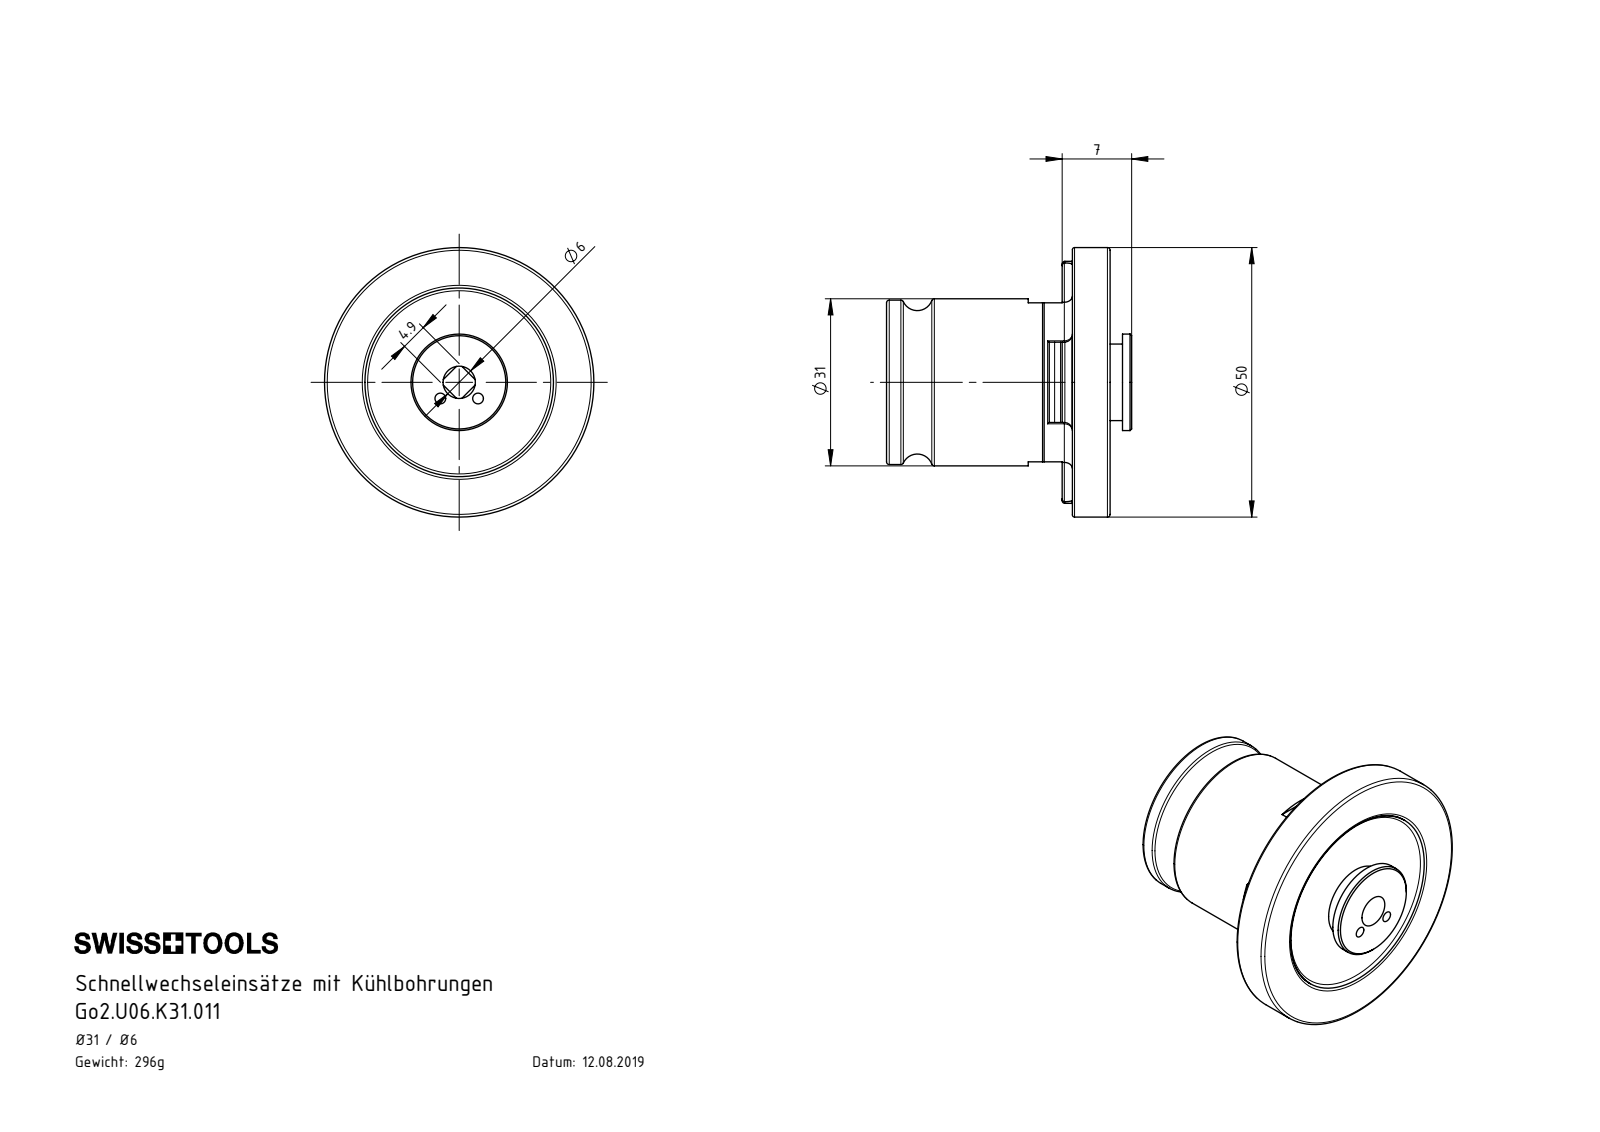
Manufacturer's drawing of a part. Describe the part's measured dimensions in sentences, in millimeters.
The part is named "Go2.U06.K31.011". Its 3-D file was written by "SolidWorks 2017 (AUTOMOTIVE_DESIGN)". It is 1 solid with 106 faces: 37 planar, 30 cylindrical and 39 other. Overall it measures 50 by 50 by 45.5 millimeters. Its volume is 37 719 cubic millimeters and its surface area 10 143 square millimeters. Round holes: 2 of diameter 2, 1 of diameter 6, 1 of diameter 20.1. Round bosses or shafts: 1 of diameter 50, 1 of diameter 35, 1 of diameter 31, 1 of diameter 30.6, 1 of diameter 30.5, 1 of diameter 17.9, 1 of diameter 14.2. Partial cylindrical surfaces (rounded edges, fillets, slot ends): 5 of radius 1.5, 4 of radius 0.5, 1 of radius 20, 1 of radius 22.45. The main face-to-face distances are 0.65, 6.35, 7, 34.5, 40.85, 41.5, 3, 31.5, 37.85, 38.5. The hole center spacings are 4.61, 7.
